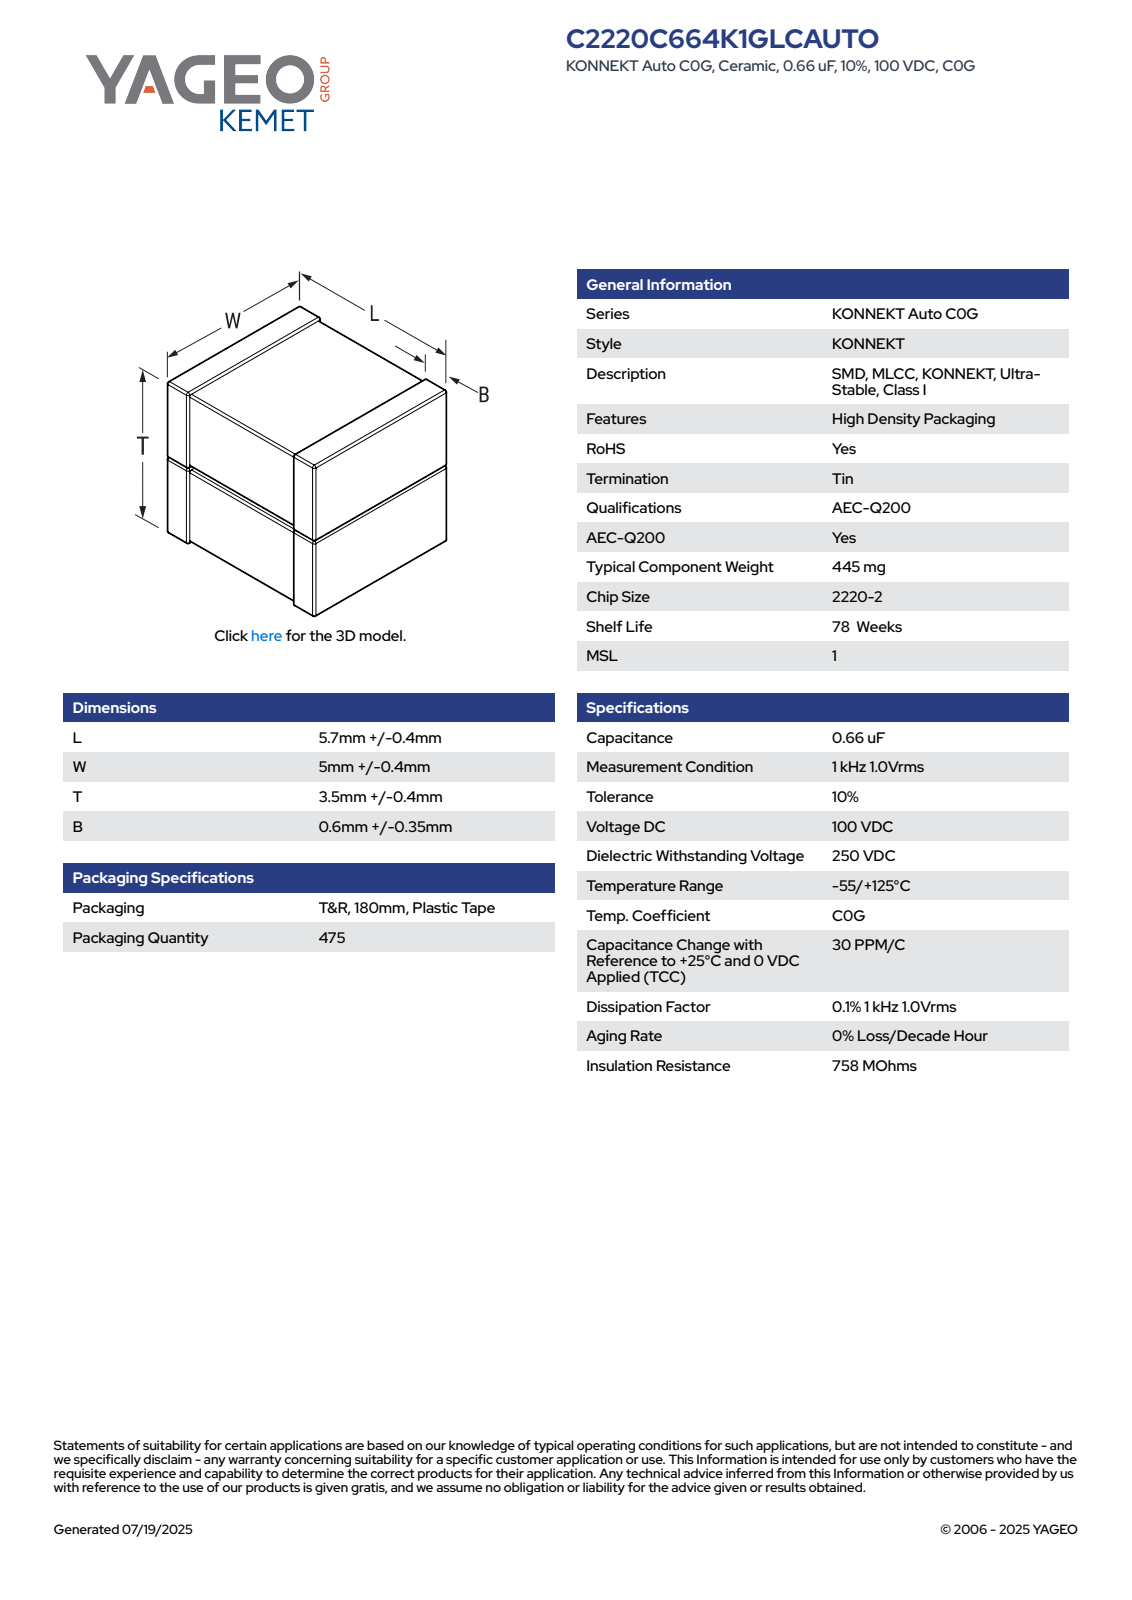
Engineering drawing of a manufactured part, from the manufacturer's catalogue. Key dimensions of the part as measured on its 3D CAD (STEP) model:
Part name (STEP PRODUCT): CCSS_K2T_2220-2_L6.1W5.4B0.95T3.9
STEP written by: SolidWorks 2020 (AUTOMOTIVE_DESIGN)
Units: millimetres
Bodies: 4 solids, 189 faces (81 planar, 76 cylindrical, 32 other)
Overall size (bounding box): 6.1 × 5.4 × 3.9
Volume: 120 mm³ · Surface area: 201 mm²
Main face-to-face distances: 1.81, 1.95, 3.76, 6.1, 2.02, 1.88, 3.83, 5.26, 5.33, 3.9
